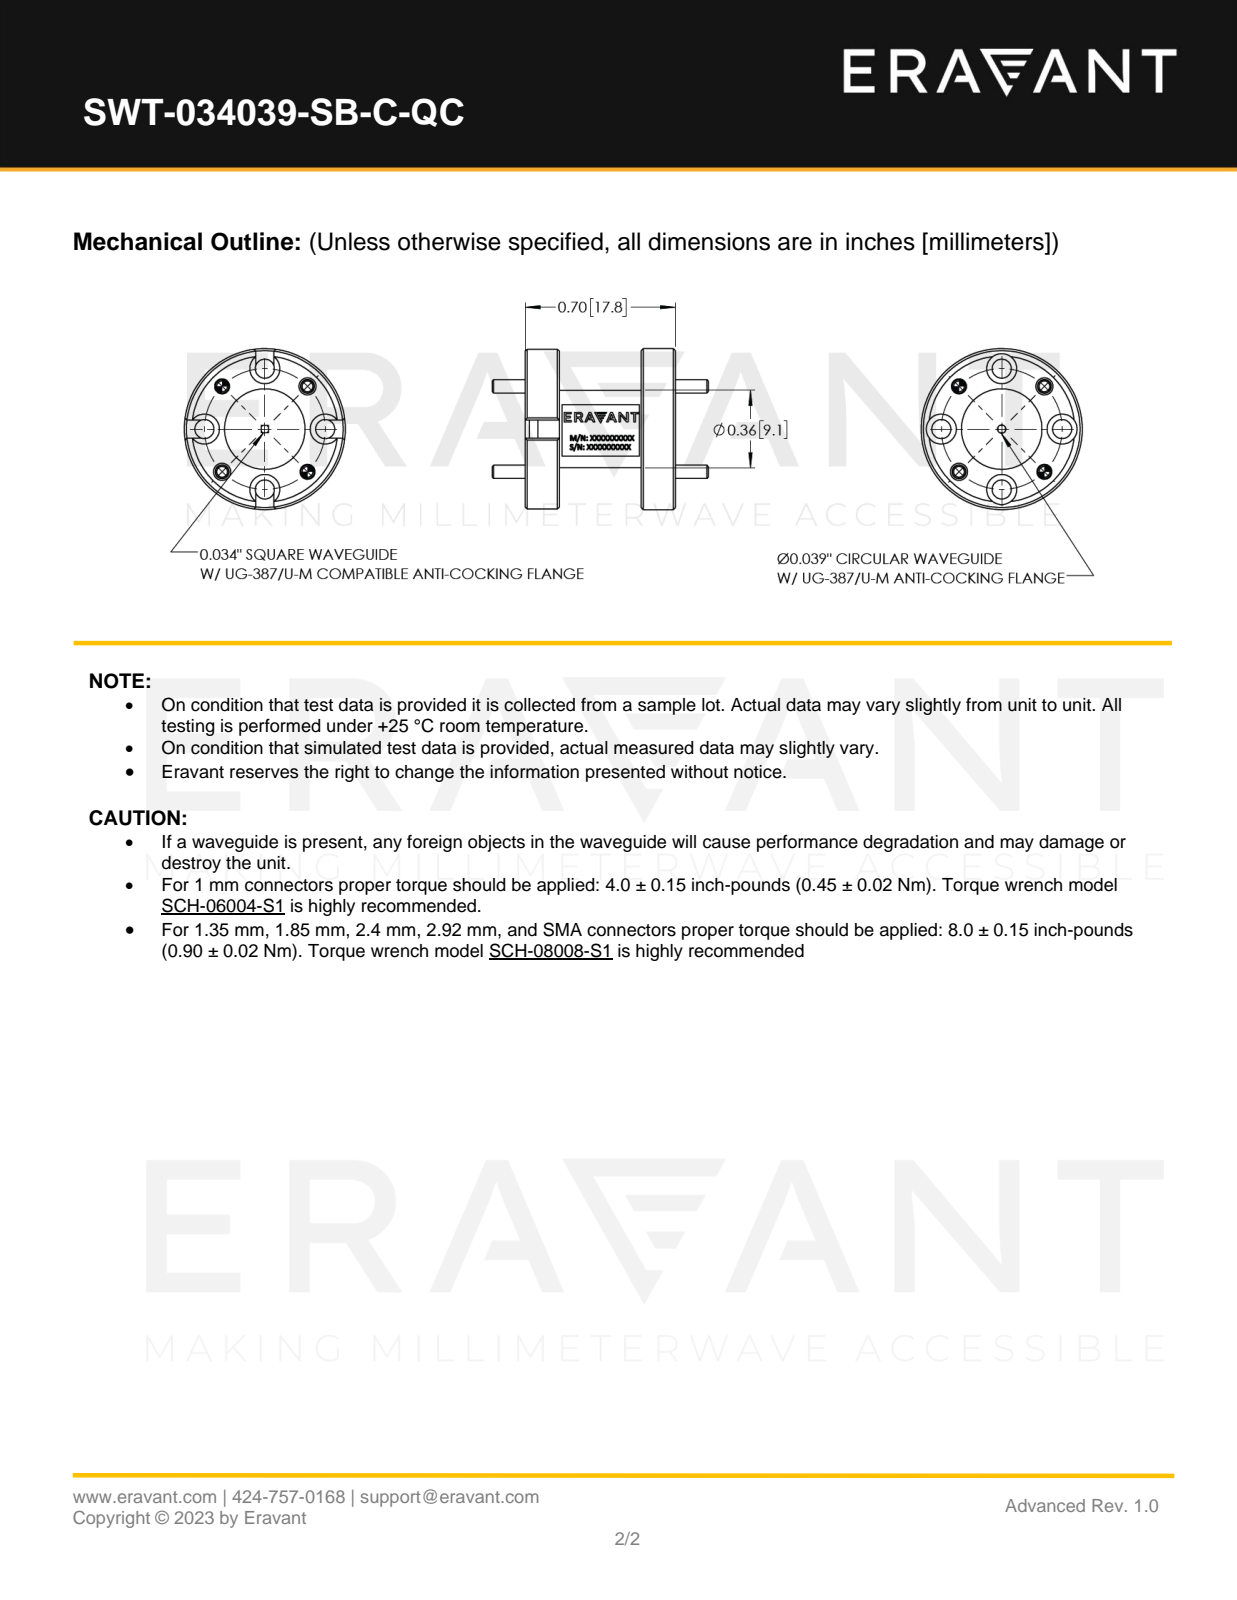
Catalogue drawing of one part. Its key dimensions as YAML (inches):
part_name: "WT-03SC-034-039-A-C"
step_written_by: "SolidWorks 2021 (CONFIG_CONTROL_DESIGN)"
units: inches
bodies: {solids: 5, faces: 175, planar: 45, cylindrical: 78, other: 52}
overall_size: [1.005, 0.75, 0.75]
volume: 0.157
surface_area: 3.439
round_holes:
  - {diameter: 0.061, count: 4}
  - {diameter: 0.064, count: 4}
  - {diameter: 0.089, count: 4}
  - {diameter: 0.14, count: 4}
  - {diameter: 0.68, count: 1}
round_bosses_or_shafts:
  - {diameter: 0.063, count: 4}
  - {diameter: 0.75, count: 1}
  - {diameter: 0.375, count: 1}
  - {diameter: 0.36, count: 1}
face_to_face_distances: [0.14, 0.52, 0.02, 0.16, 0.54, 0.68, 0.38, 0.66, 0.7, 0.06]
hole_center_spacings: [0.215, 0.281, 0.398, 0.519, 0.562]
